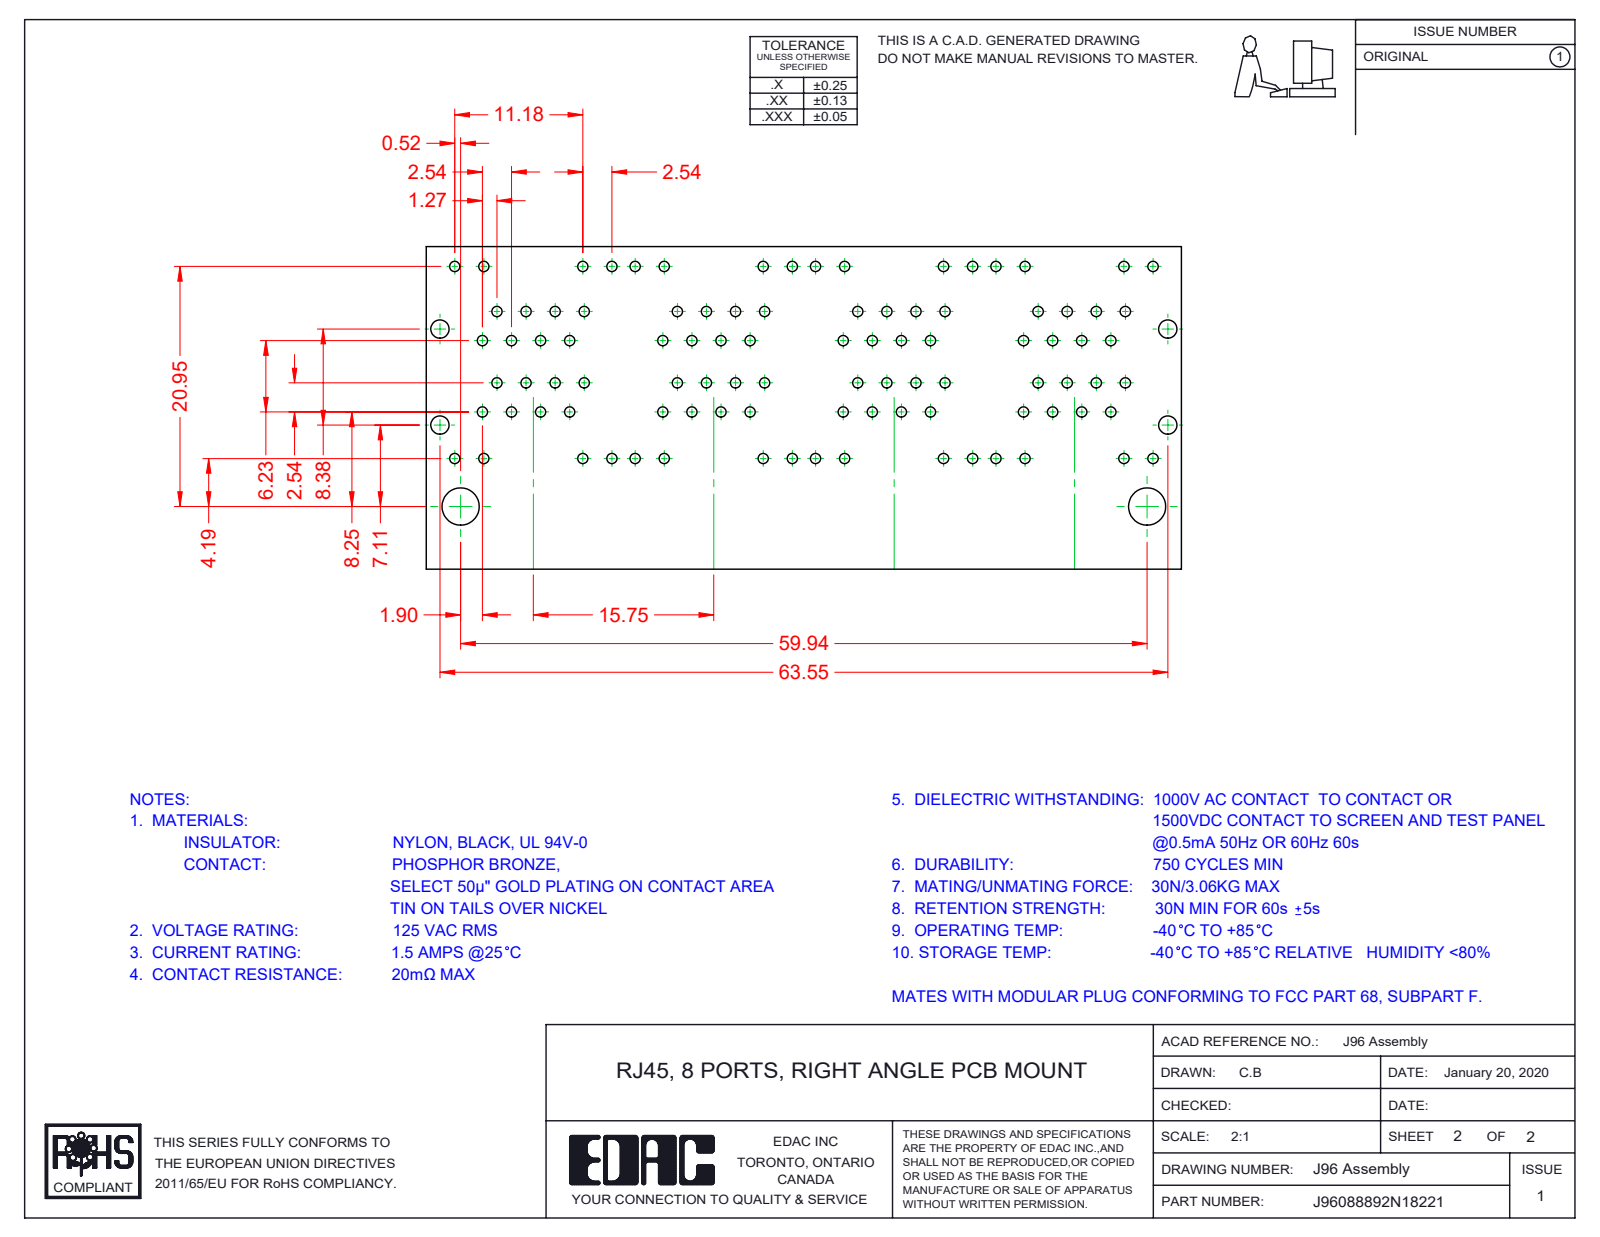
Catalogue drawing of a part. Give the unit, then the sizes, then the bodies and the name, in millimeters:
Units: millimetres
Overall size (bounding box): 67.35 × 31.38 × 28.68
Round holes (diameter × count): ⌀1.7 ×3
Round bosses / shafts (diameter × count): ⌀1.68 ×3
Partial cylindrical surfaces — rounded edges, fillets, slot ends (radius × count): R0.25 ×124, R0.35 ×73, R1 ×72, R0.5 ×49, R0.91 ×32, R0.2 ×27, R0.27 ×14, R0.7 ×11
Main face-to-face distances: 15.75, 0.35, 9.95, 1.17, 1.6, 0.54, 9.98, 10.18, 12.67, 3.37
Hole centre spacings: 15.75, 31.5
Volume: 24 149 mm³ · Surface area: 63 596 mm²
Bodies: 96 solids, 7820 faces (6105 planar, 1404 cylindrical, 311 other)
Part name (STEP PRODUCT): 96 Shield_8 Ports LED - EMI; 96 Contact Lock Upper; 96 Insulator Insert; J96088892N18221 (+8 more)
STEP written by: SolidWorks 2016 (CONFIG_CONTROL_DESIGN)
